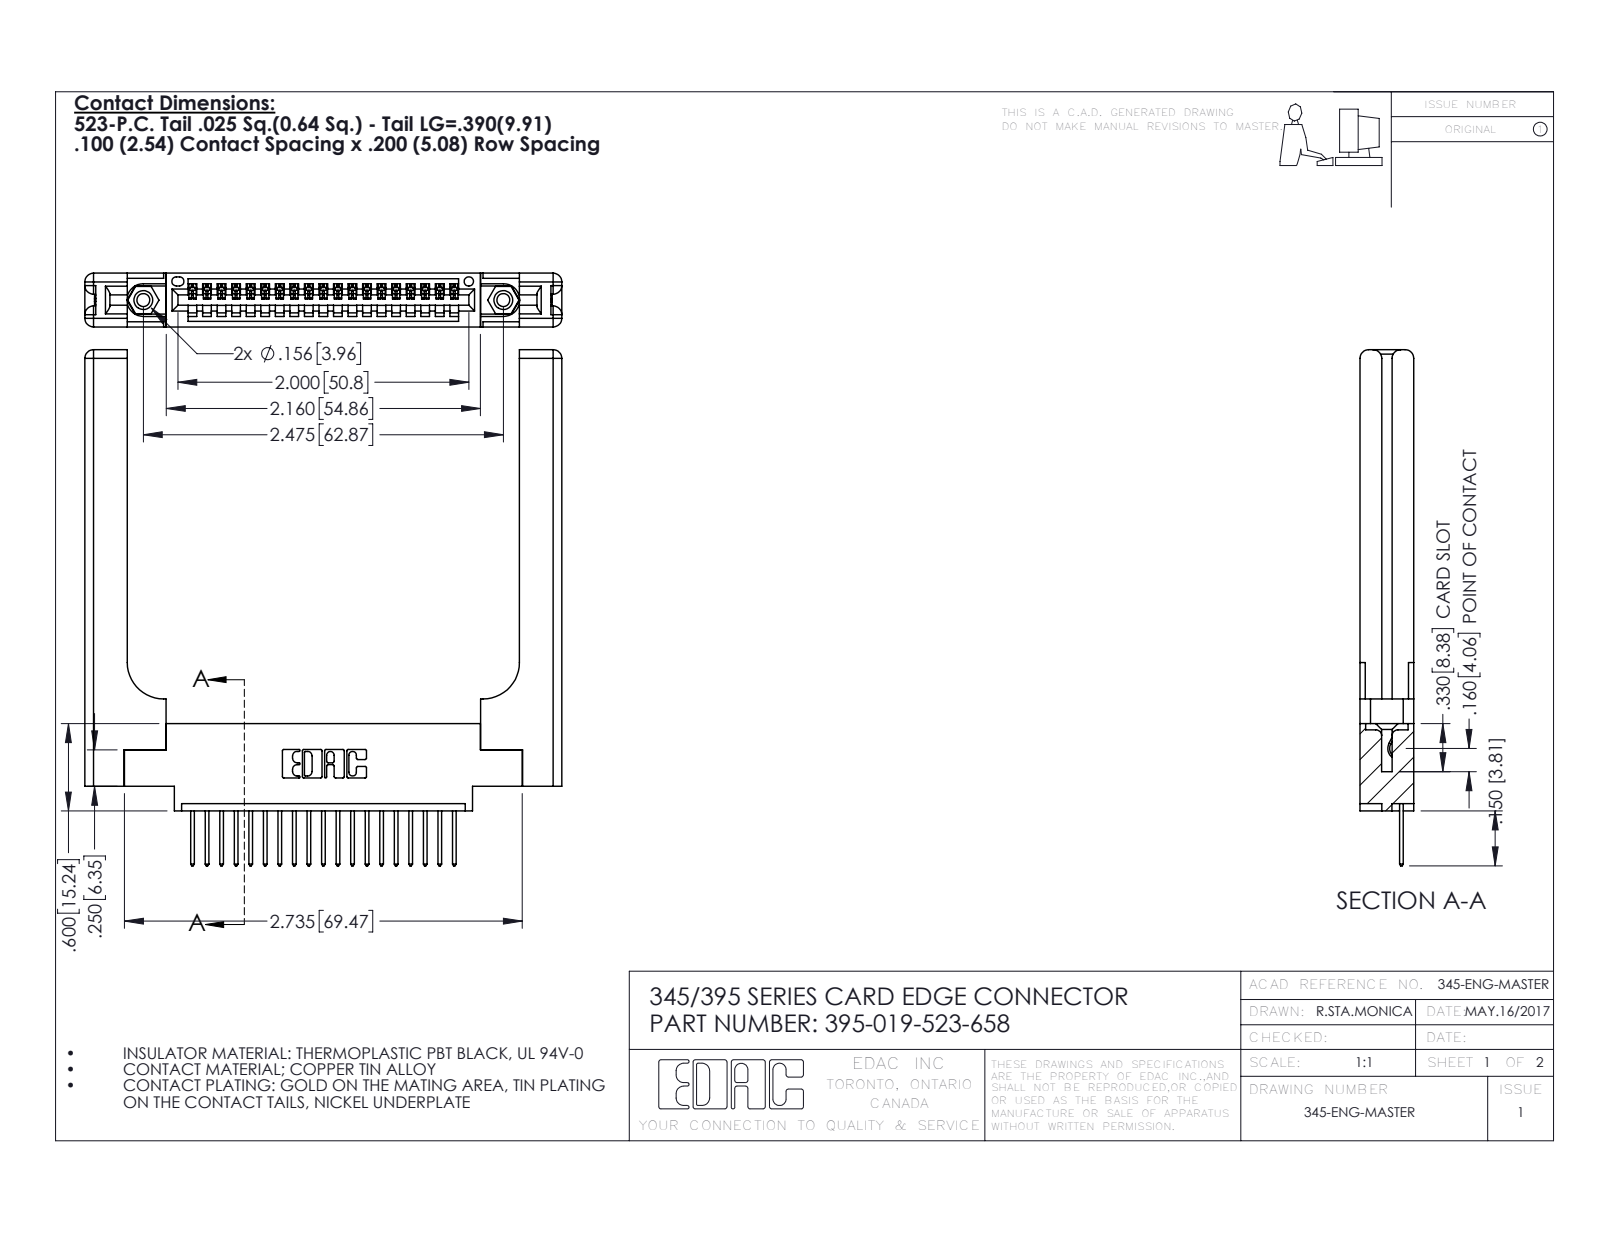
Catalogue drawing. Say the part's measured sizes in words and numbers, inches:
The part is named "345-250-001_345-250-001-102; 345 Part_0.170 Offset - 0.156 Dia-TH; 345-220-058_345-220-058; 345-292-001_345-293-123 (+1 more)". Its 3-D file was written by "SolidWorks 2016 (CONFIG_CONTROL_DESIGN)". It is 24 solids with 1488 faces: 992 planar, 436 cylindrical and 60 other. Overall it measures 3.547 by 3.279 by 0.37 inches. Its volume is 0.983 cubic inches and its surface area 23.63 square inches. Round holes: 2 of diameter 0.089, 2 of diameter 0.125, 2 of diameter 0.156, 1 of diameter 0.064. Round bosses or shafts: 2 of diameter 0.155. Partial cylindrical surfaces (rounded edges, fillets, slot ends): 38 of radius 0.006, 38 of radius 0.01, 22 of radius 0.01, 16 of radius 0.06, 6 of radius 0.007, 6 of radius 0.031, 3 of radius 0.026, 2 of radius 0.03. The main face-to-face distances are 0.37, 0.072, 0.298, 0.15, 0.148, 0.077, 0.22, 0.098, 0.272, 0.025. The hole center spacings are 0.27, 2.241, 2.475.
